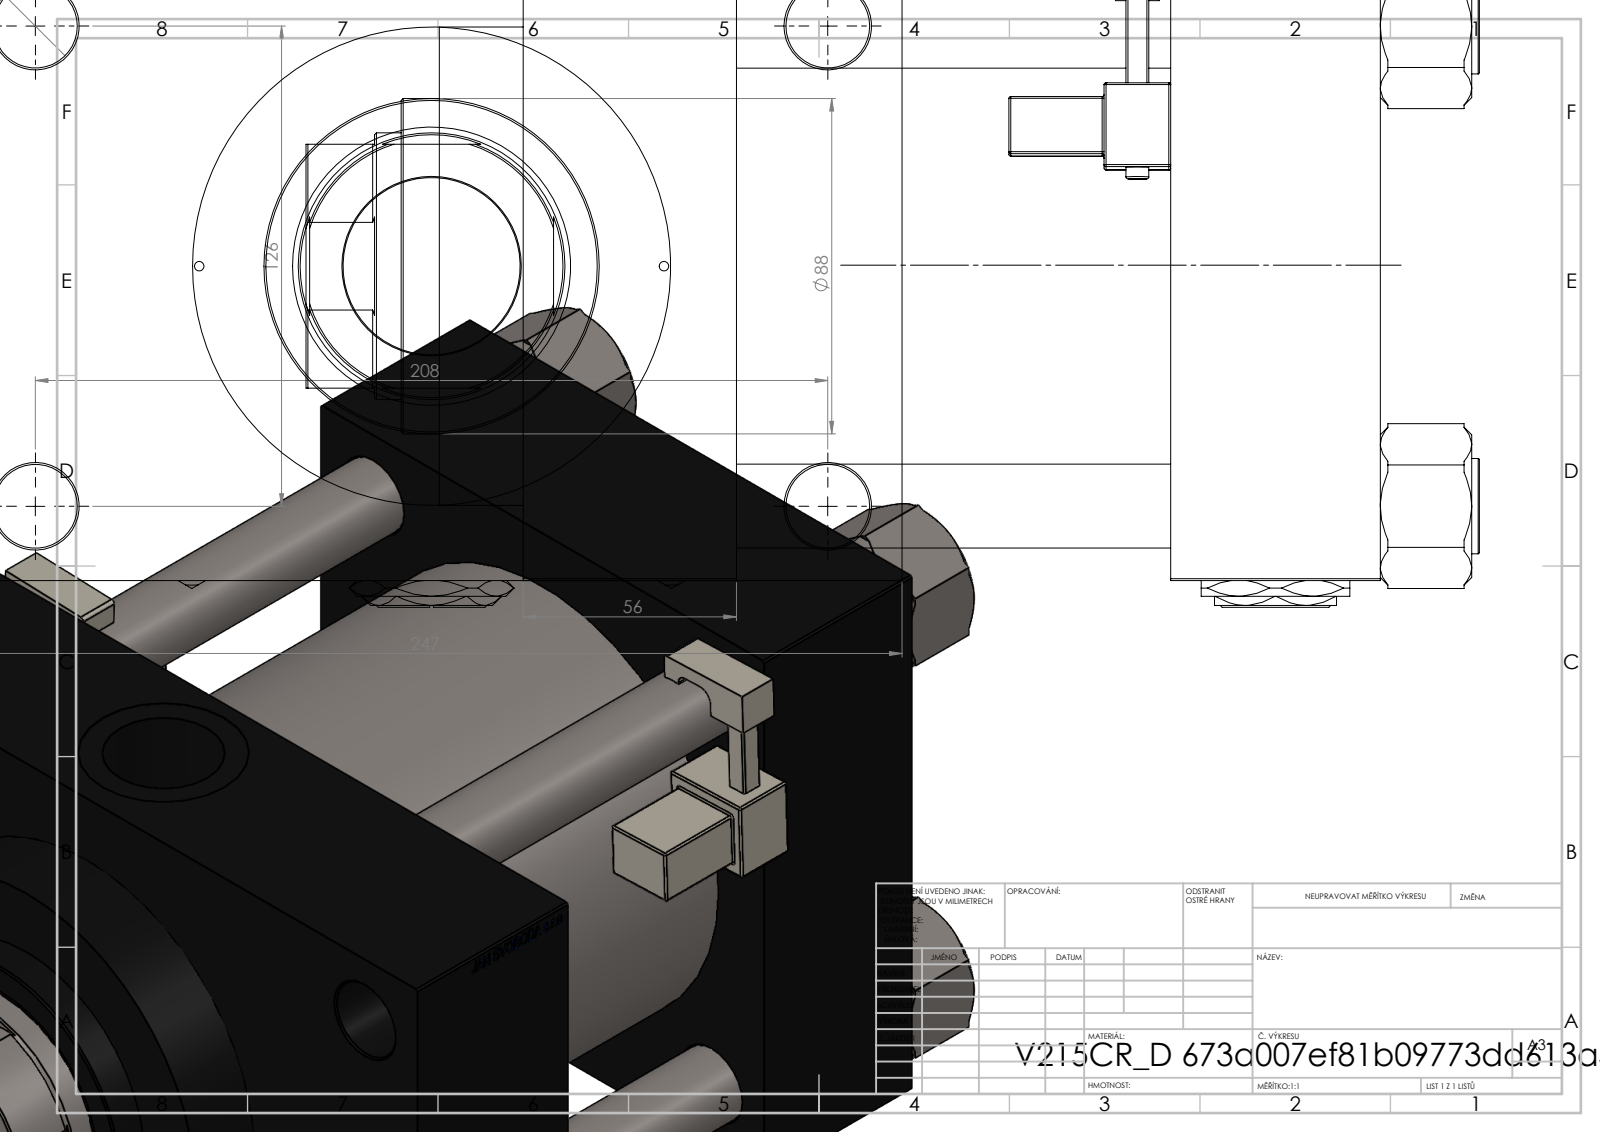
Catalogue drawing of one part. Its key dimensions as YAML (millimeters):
part_name: "NUT_M5_D; Zatka_pro_OIL_PORT; V215CR_D_Body; V215CR_MSU (+3 more)"
step_written_by: "SolidWorks 2019 (CONFIG_CONTROL_DESIGN)"
units: millimeters
bodies: {solids: 14, faces: 1351, planar: 626, cylindrical: 151, other: 574}
overall_size: [308, 247, 174.07]
volume: 5289000
surface_area: 593336
round_holes:
  - {diameter: 22, count: 8}
  - {diameter: 2.5, count: 2}
  - {diameter: 7, count: 2}
  - {diameter: 32.24, count: 2}
  - {diameter: 45, count: 2}
  - {diameter: 46.5, count: 1}
  - {diameter: 70, count: 1}
  - {diameter: 73, count: 1}
  - {diameter: 96, count: 1}
  - {diameter: 125, count: 1}
  - {diameter: 125.5, count: 1}
round_bosses_or_shafts:
  - {diameter: 25, count: 4}
  - {diameter: 6, count: 2}
  - {diameter: 131, count: 1}
  - {diameter: 88, count: 1}
partial_cylinders:
  - {radius: 0.5, count: 48}
  - {radius: 1, count: 2}
  - {radius: 2.5, count: 2}
  - {radius: 4, count: 2}
  - {radius: 34, count: 1}
face_to_face_distances: [165, 114, 169, 55, 170, 56, 225, 41, 206, 247]
hole_center_spacings: [41.05, 62.98, 76.28, 89.02, 121.59, 125.9, 132.47, 139.02]
